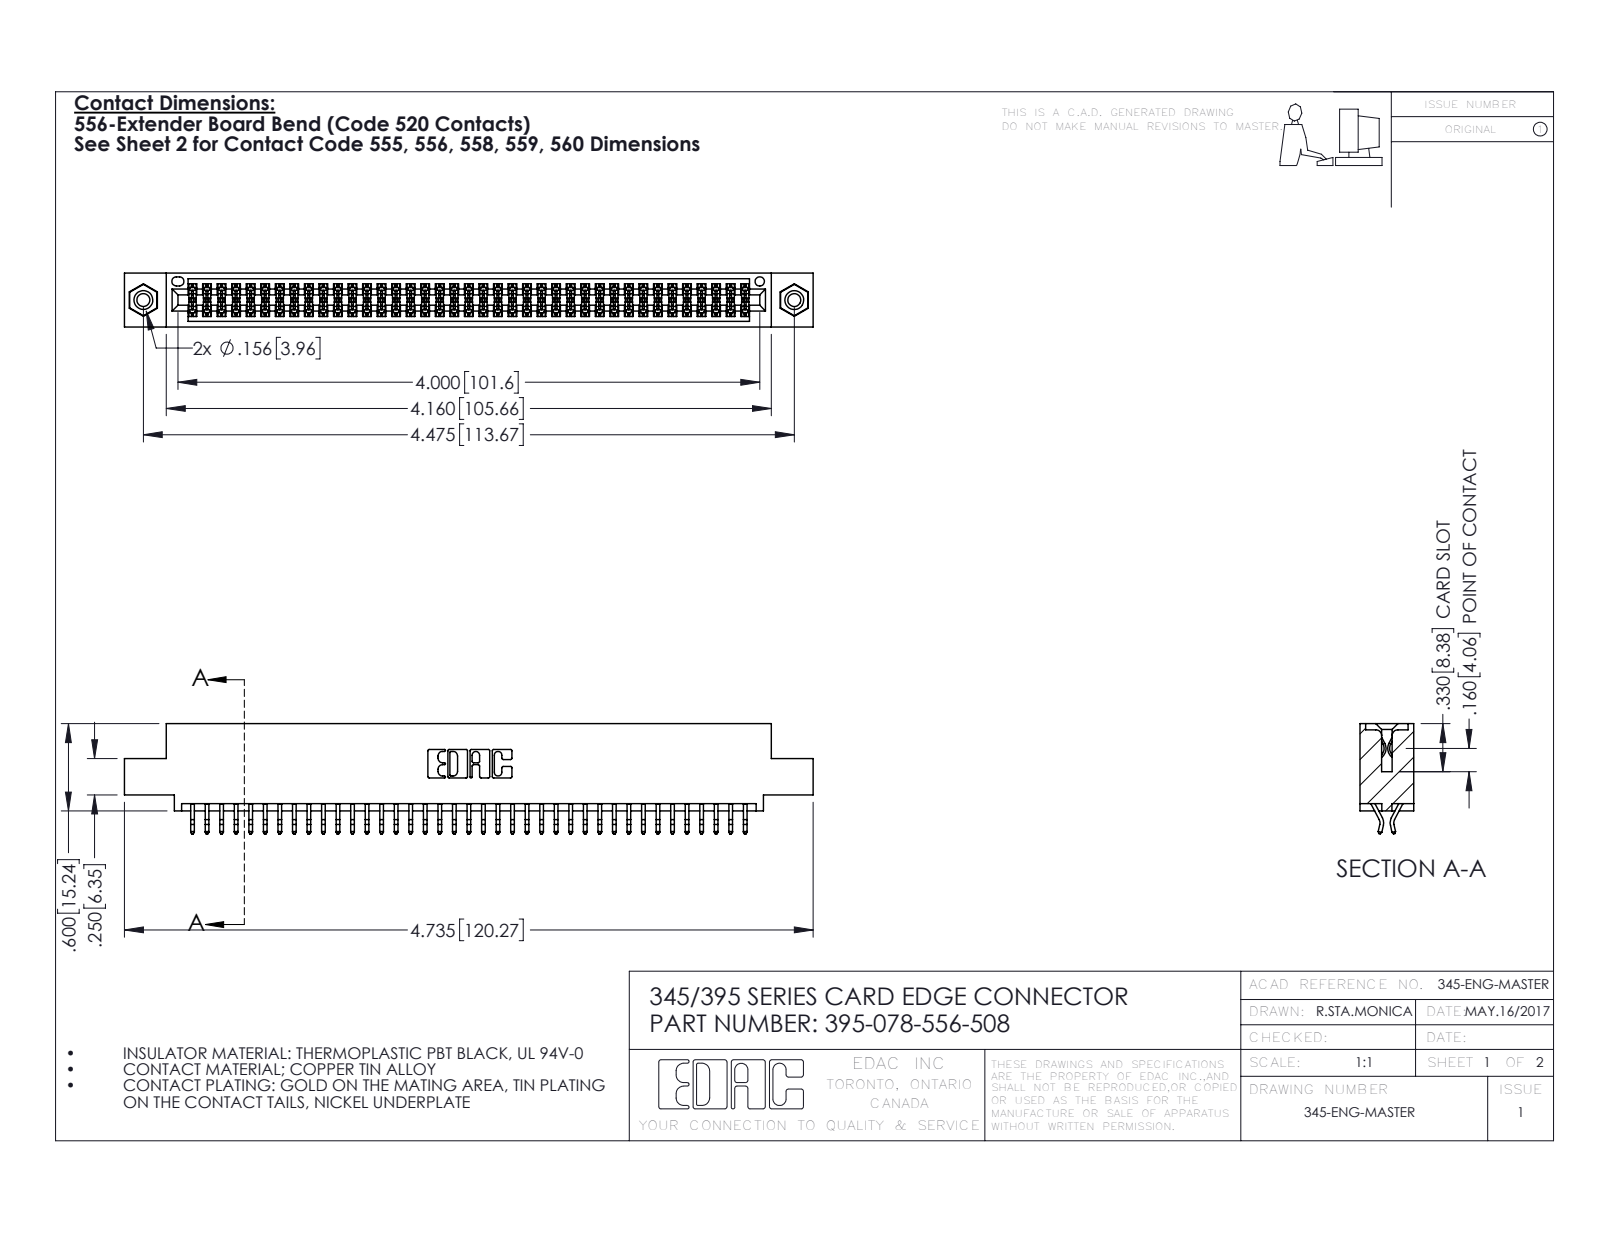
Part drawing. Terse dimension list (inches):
name: 395-078-556-508; 345-250-001_345-250-003-102; 345-292-001_556 Tail; 345 Part_0.110 Offset - 0.156 Dia-TI
written by: SolidWorks 2016 (CONFIG_CONTROL_DESIGN)
unit: in
bodies: 81 solids, 4558 faces (3002 planar, 1540 cylindrical, 16 other)
size: 4.735 × 0.757 × 0.37
volume: 0.706 in³; area: 26.48 in²
holes: 2× ⌀0.089, 2× ⌀0.125, 2× ⌀0.156, 1× ⌀0.064
bosses: 2× ⌀0.155
rounds: 117× R0.006, 22× R0.01, 6× R0.007, 6× R0.031, 3× R0.026, 2× R0.01, 2× R0.014, 2× R0.019
face distances: 0.072, 0.298, 0.37, 0.2, 0.025, 0.098, 0.272, 0.225, 0.175, 0.149
hole spacings: 0.27, 4.239, 4.475
